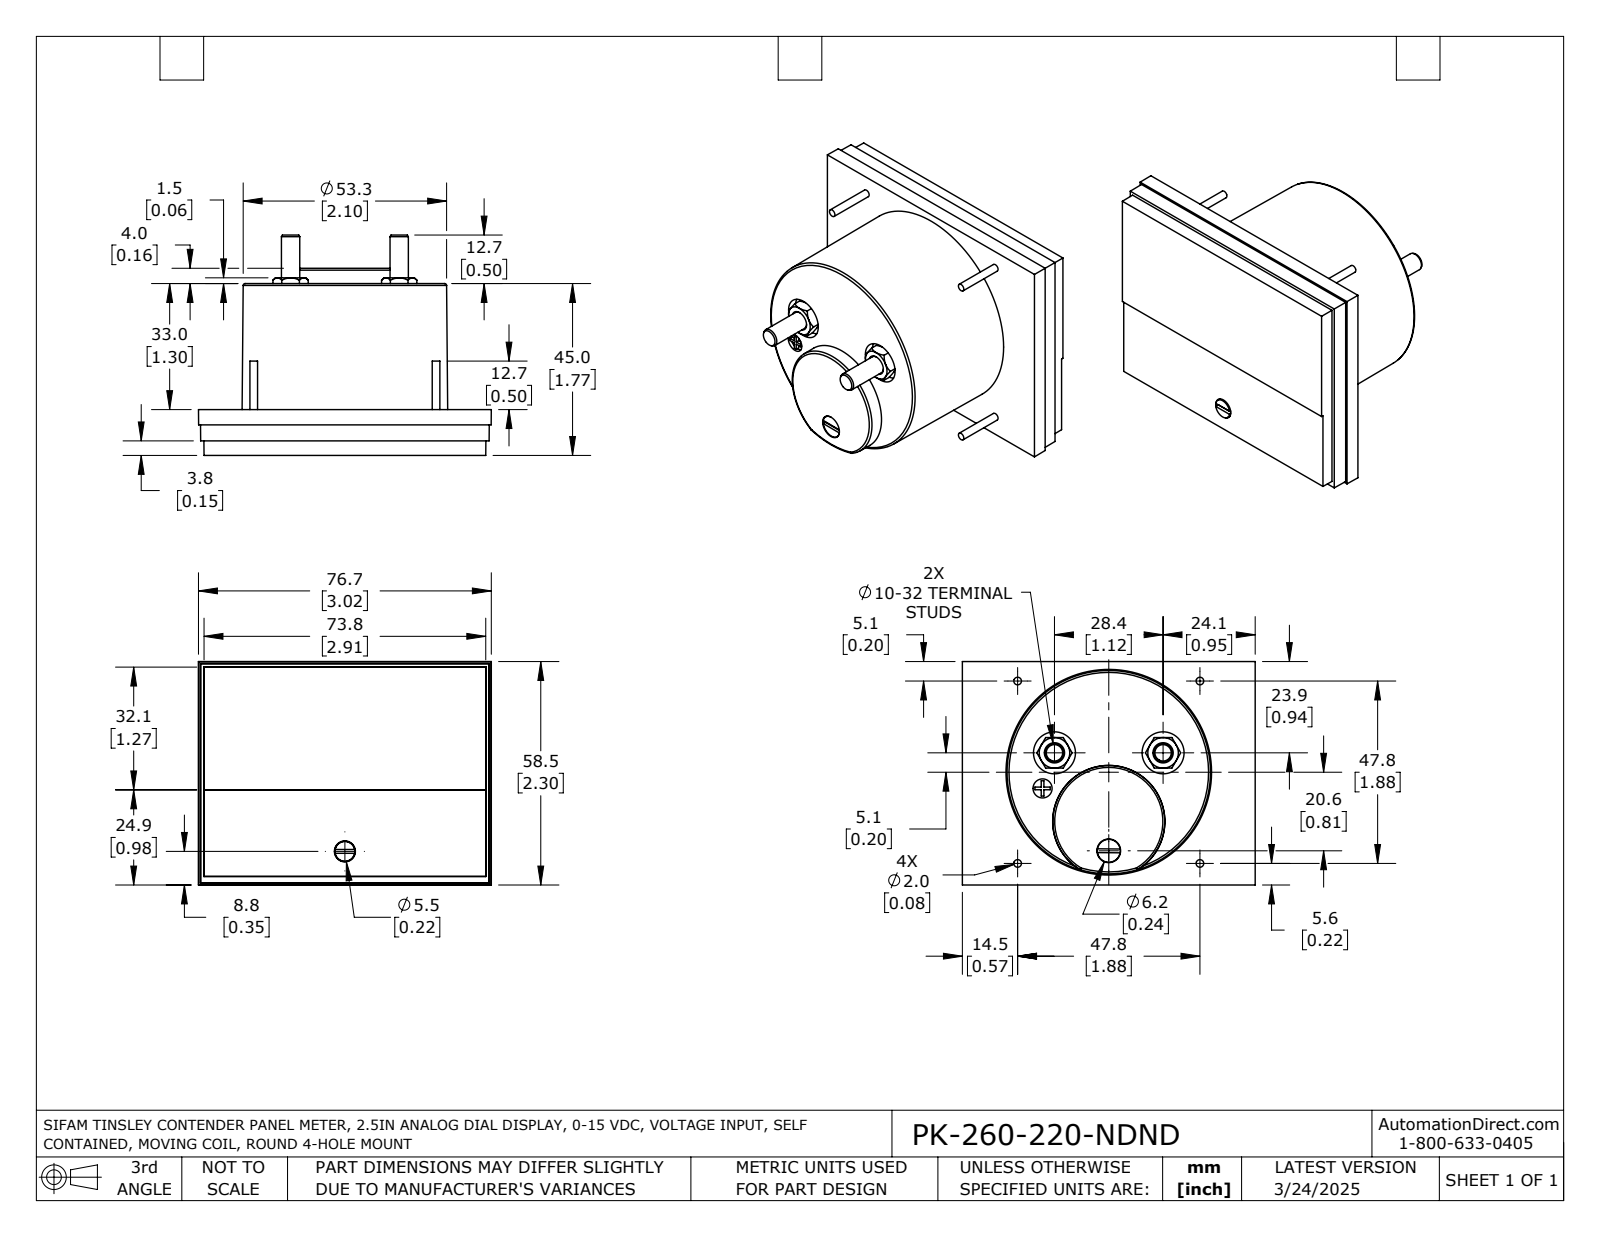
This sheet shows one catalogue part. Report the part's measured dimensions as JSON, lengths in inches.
{"part_name": "PK-260-220-NDND", "step_written_by": "SolidWorks 2021 (AUTOMOTIVE_DESIGN)", "units": "inches", "bodies": {"solids": 1, "faces": 192, "planar": 95, "cylindrical": 37, "other": 60}, "overall_size": [3.02, 2.303, 2.272], "volume_in3": 7.657, "surface_area_in2": 36.55, "round_holes": [[0.197, 3], [0.433, 2], [0.209, 1], [0.217, 1], [0.244, 1]], "round_bosses_or_shafts": [[0.079, 4], [0.189, 2], [0.236, 1], [0.205, 1]], "partial_cylinders_radius": [[0.033, 1]], "face_to_face_distances": [0.02, 0.472, 0.13, 0.322, 0.15, 0.453, 0.057, 0.077, 0.396, 0.073], "hole_center_spacings": [1.155, 1.16, 0.387, 0.938, 0.942, 1.12, 1.295]}
